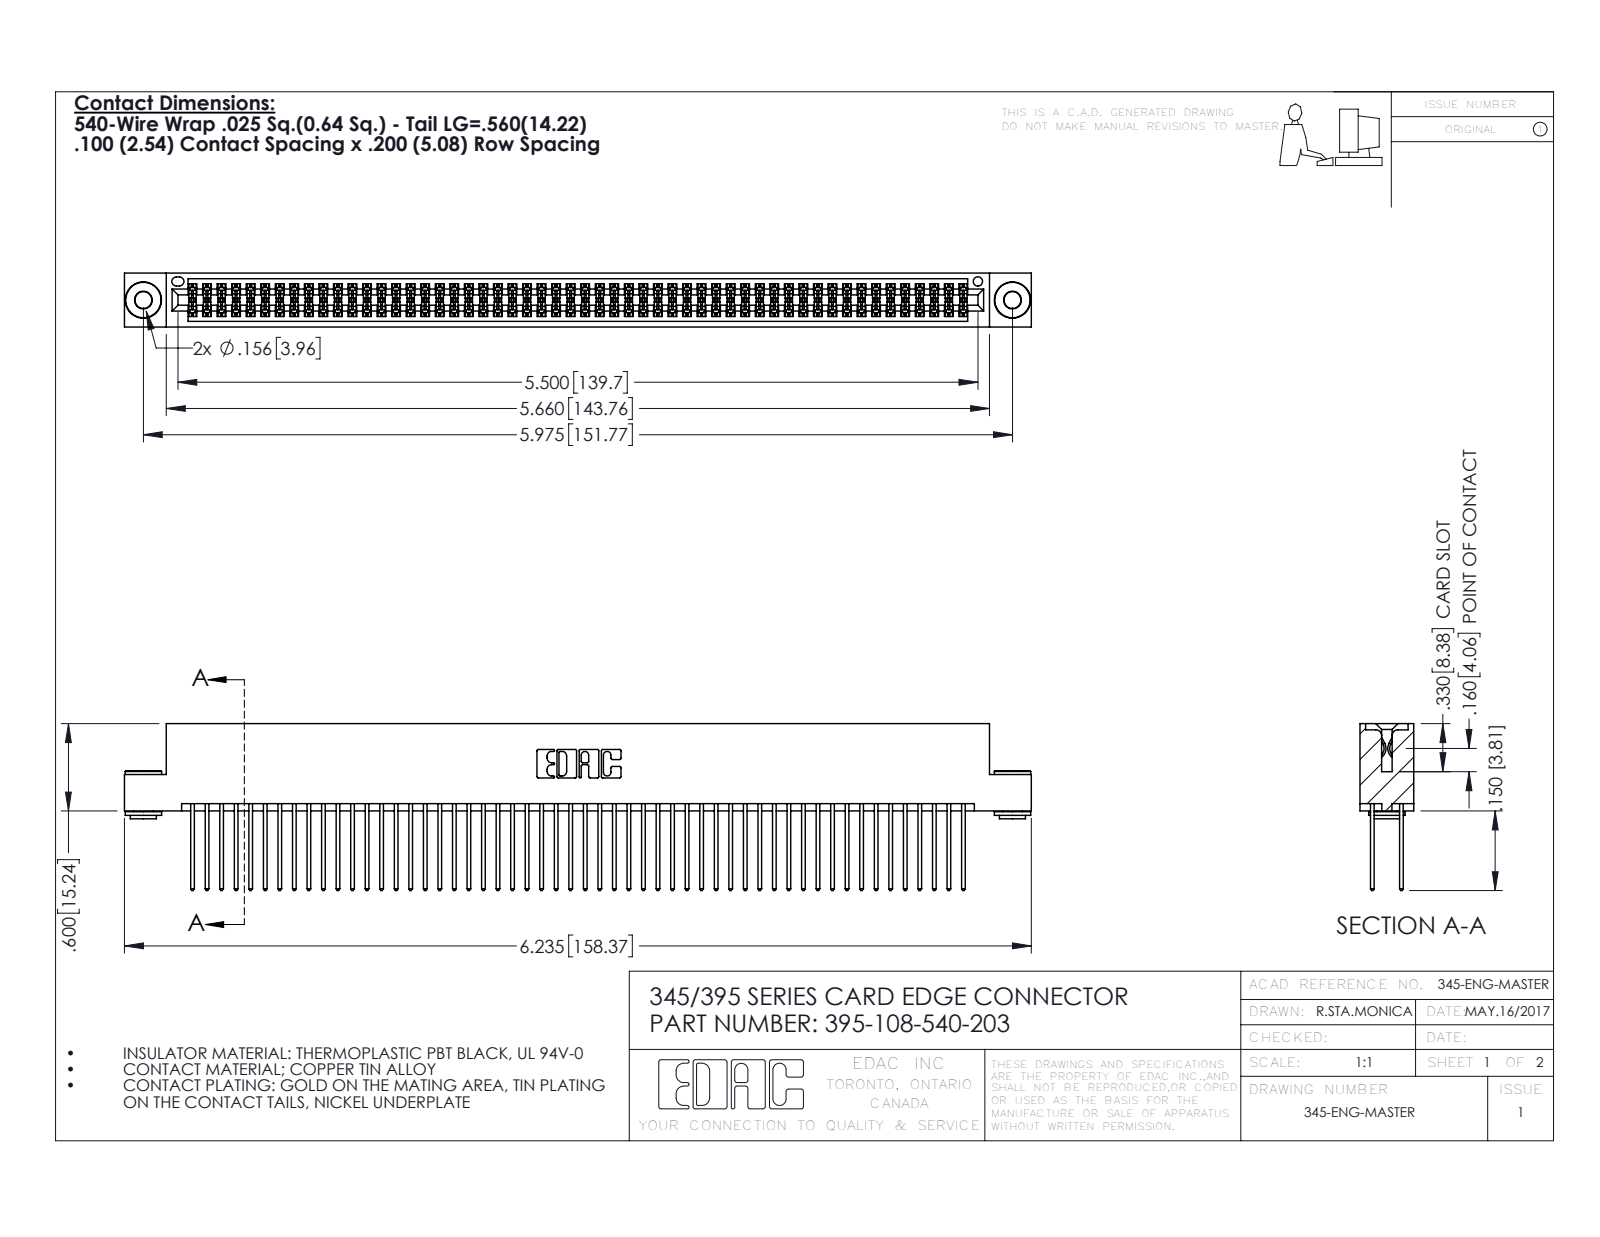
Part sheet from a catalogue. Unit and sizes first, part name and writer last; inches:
Units: inches
Overall size (bounding box): 6.235 × 1.147 × 0.37
Round holes (diameter × count): ⌀0.116 ×2, ⌀0.156 ×2, ⌀0.064 ×1
Round bosses / shafts (diameter × count): ⌀0.25 ×2, ⌀0.18 ×2, ⌀0.136 ×2
Partial cylindrical surfaces — rounded edges, fillets, slot ends (radius × count): R0.006 ×162, R0.01 ×108, R0.01 ×22, R0.007 ×6, R0.031 ×6, R0.026 ×3, R0.014 ×2, R0.019 ×2
Main face-to-face distances: 0.072, 0.298, 0.2, 0.025, 0.098, 0.272, 0.225, 0.37, 0.175, 0.149
Hole centre spacings: 0.27, 5.739, 5.975
Volume: 0.972 in³ · Surface area: 40.11 in²
Bodies: 111 solids, 5564 faces (3654 planar, 1902 cylindrical, 8 other)
Part name (STEP PRODUCT): 395-108-540-203; 345-250-002_345-250-002-102; 345 Part_Flush Mounting Lugs - 0.156 Dia-TH; 345-292-001_345-293-140
STEP written by: SolidWorks 2016 (CONFIG_CONTROL_DESIGN)
